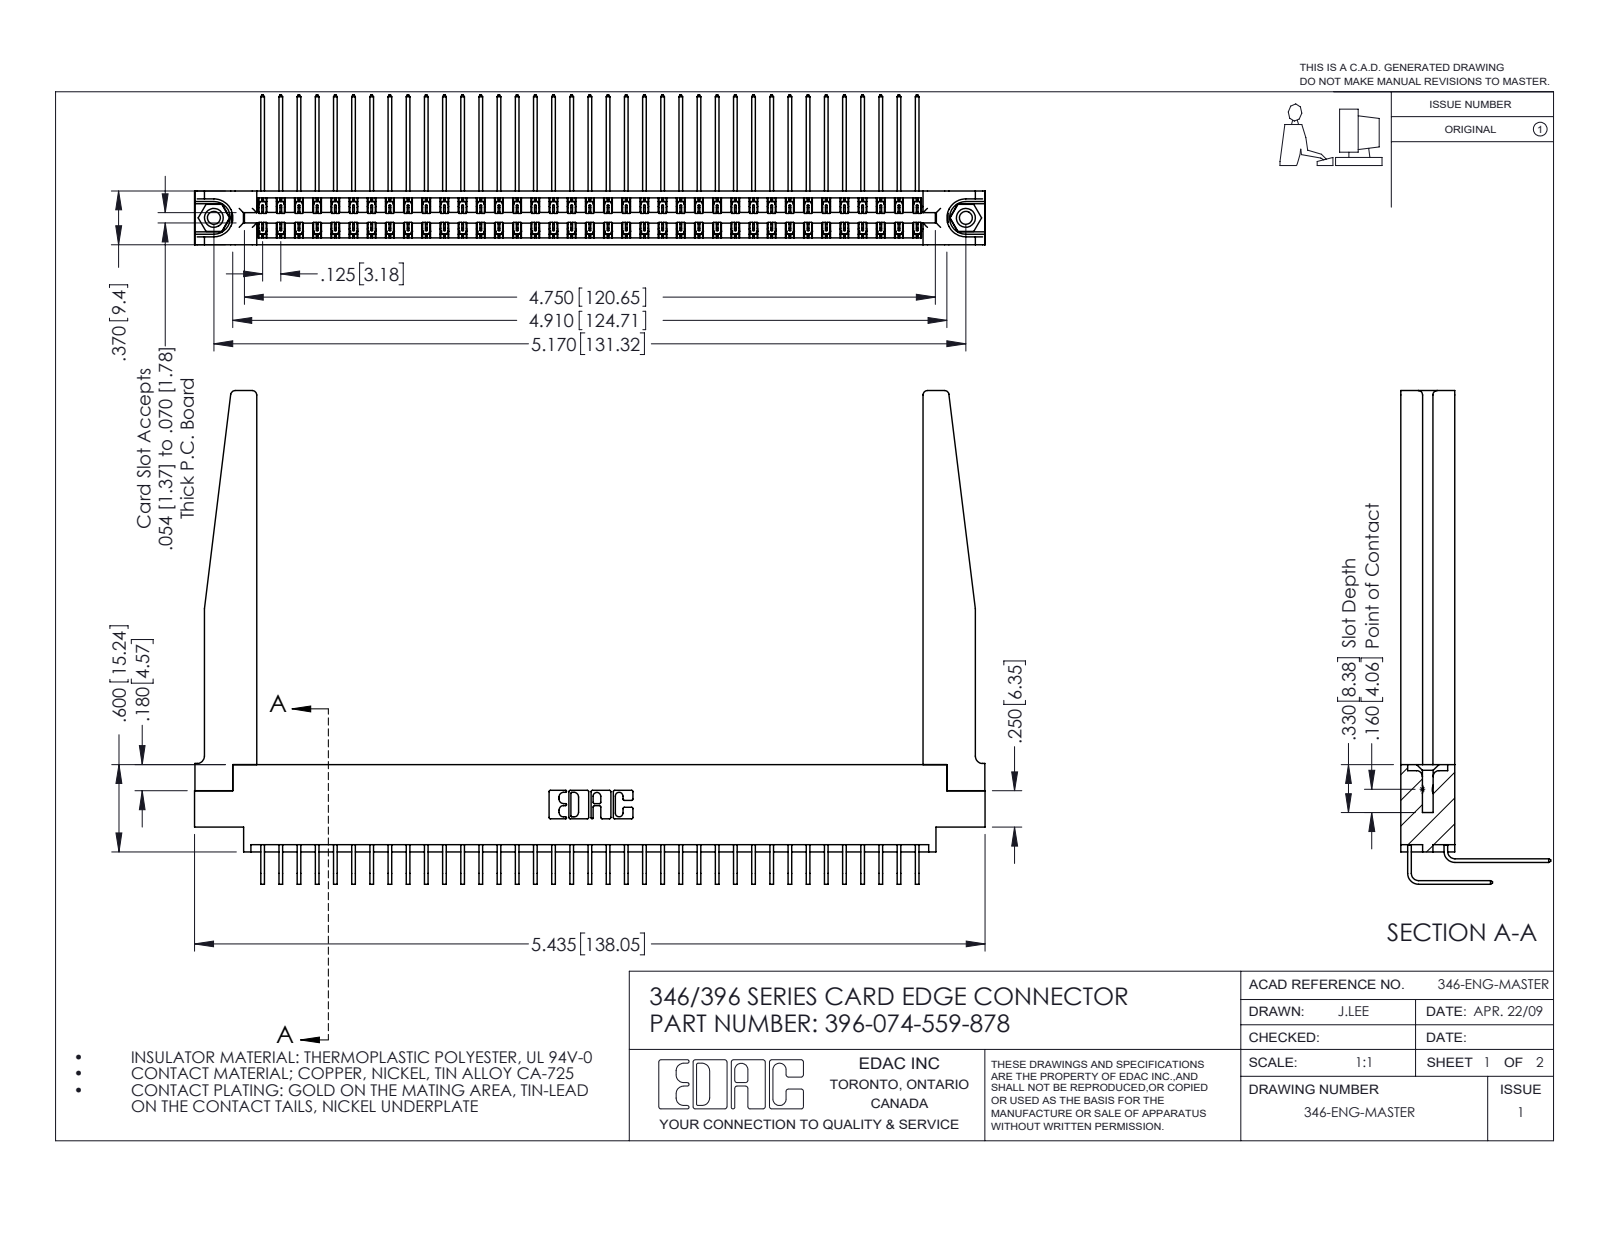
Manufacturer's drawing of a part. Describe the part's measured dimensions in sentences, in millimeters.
The part is named "345-292-001_558 559 Tail - 1; 345-292-001_559 Tail - 2; 346 Part_0.170 Offset - 0.156 Dia-TH; 396-074-559-878 (+2 more)". Its 3-D file was written by "SolidWorks 2016 (CONFIG_CONTROL_DESIGN)". It is 79 solids with 4356 faces: 2960 planar, 1344 cylindrical and 52 other. Overall it measures 138 by 86.2 by 26.2 millimeters. Its volume is 20 600 cubic millimeters and its surface area 27 510 square millimeters. Round holes: 2 of diameter 2.3, 2 of diameter 3.2, 2 of diameter 4, 1 of diameter 1.6. Round bosses or shafts: 2 of diameter 3.9. Partial cylindrical surfaces (rounded edges, fillets, slot ends): 111 of radius 0.2, 22 of radius 0.3, 8 of radius 0.8, 6 of radius 0.2, 6 of radius 0.8, 4 of radius 1.3, 3 of radius 0.7, 2 of radius 0.4. The main face-to-face distances are 9.4, 1.2, 8.2, 1.8, 0.6, 3.8, 3.8, 6.4, 7.6, 7. The hole center spacings are 6.2, 126, 131.3.
